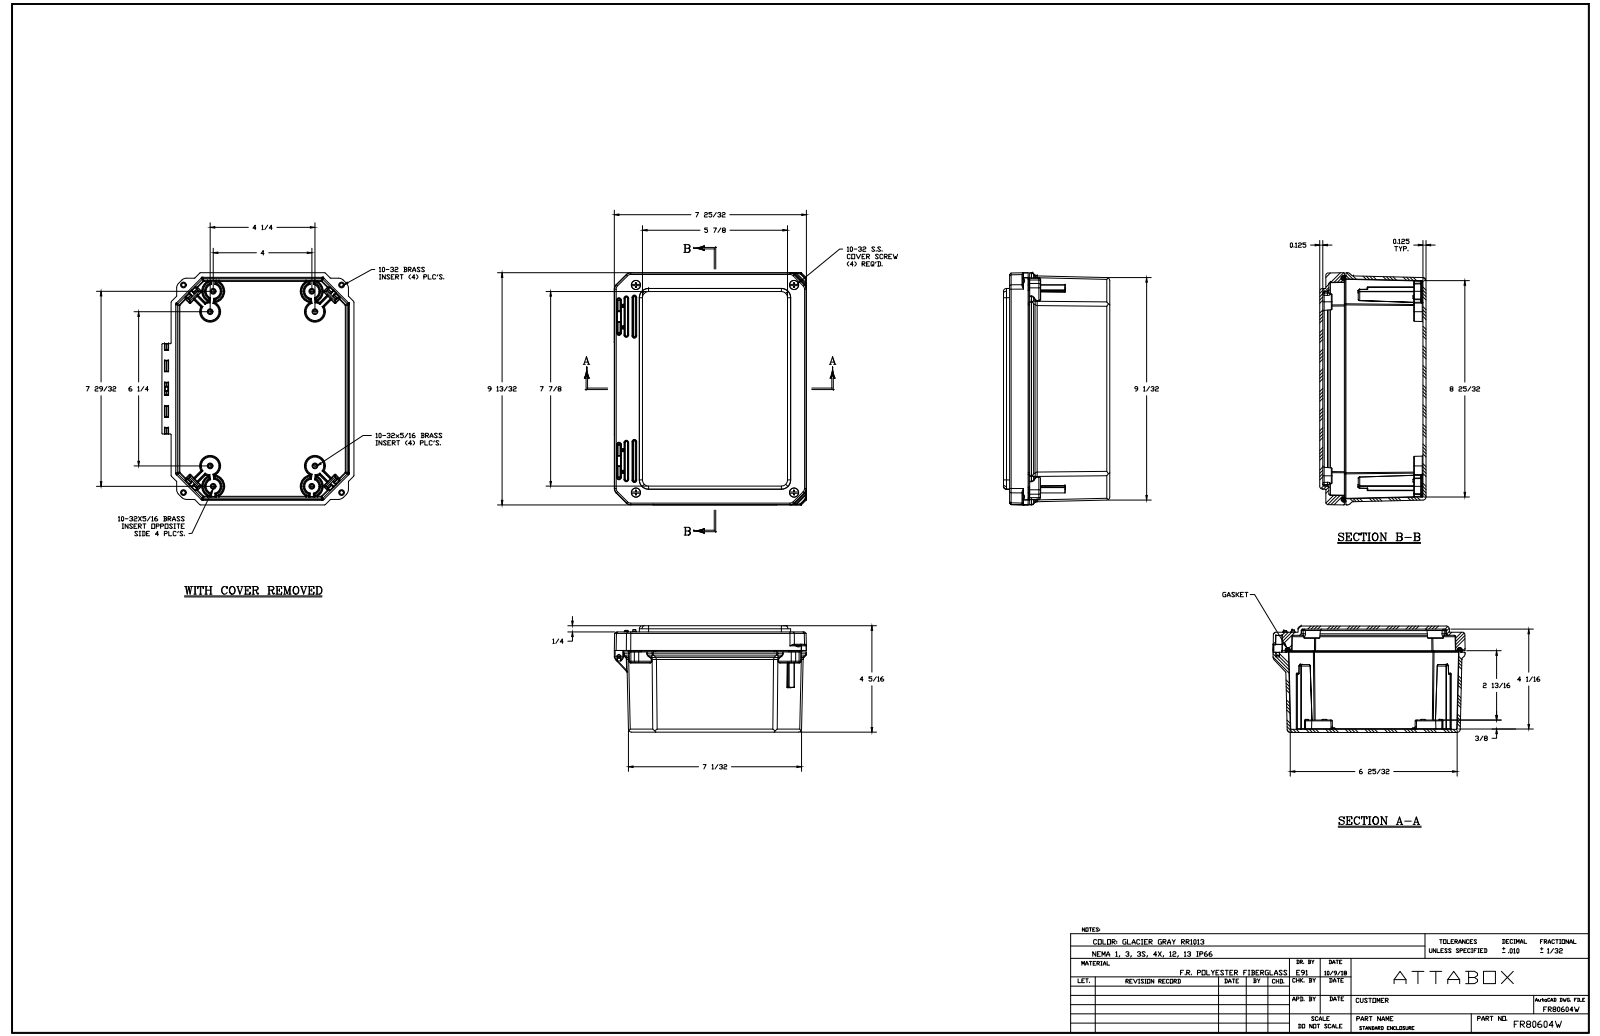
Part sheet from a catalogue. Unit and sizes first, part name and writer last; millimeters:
Units: millimetres
Overall size (bounding box): 239.6 × 197.9 × 109.5
Round holes (diameter × count): ⌀4 ×16, ⌀3.9 ×8, ⌀6.4 ×4, ⌀6.4 ×4, ⌀5.6 ×2, ⌀5.8 ×2, ⌀8 ×2, ⌀3.5 ×1
Round bosses / shafts (diameter × count): ⌀6.2 ×16, ⌀22.1 ×4, ⌀11.4 ×4, ⌀5.1 ×4, ⌀11 ×2
Partial cylindrical surfaces — rounded edges, fillets, slot ends (radius × count): R0.3 ×104, R0.1 ×80, R0.5 ×65, R0.8 ×42, R0.8 ×24, R2.3 ×24, R2.4 ×24, R3.2 ×22
Main face-to-face distances: 3.2, 106.3, 109.5, 103.1, 6.4, 3.1, 99.9, 3.2, 103.1, 9.5
Hole centre spacings: 208.1, 230.3, 38.9, 21.3, 31.3, 106.9, 108, 132.4
Volume: 723 800 mm³ · Surface area: 388 900 mm²
Bodies: 27 solids, 2010 faces (675 planar, 721 cylindrical, 614 other)
Part name (STEP PRODUCT): FR80604W
STEP written by: SolidWorks 2018 (AUTOMOTIVE_DESIGN)
